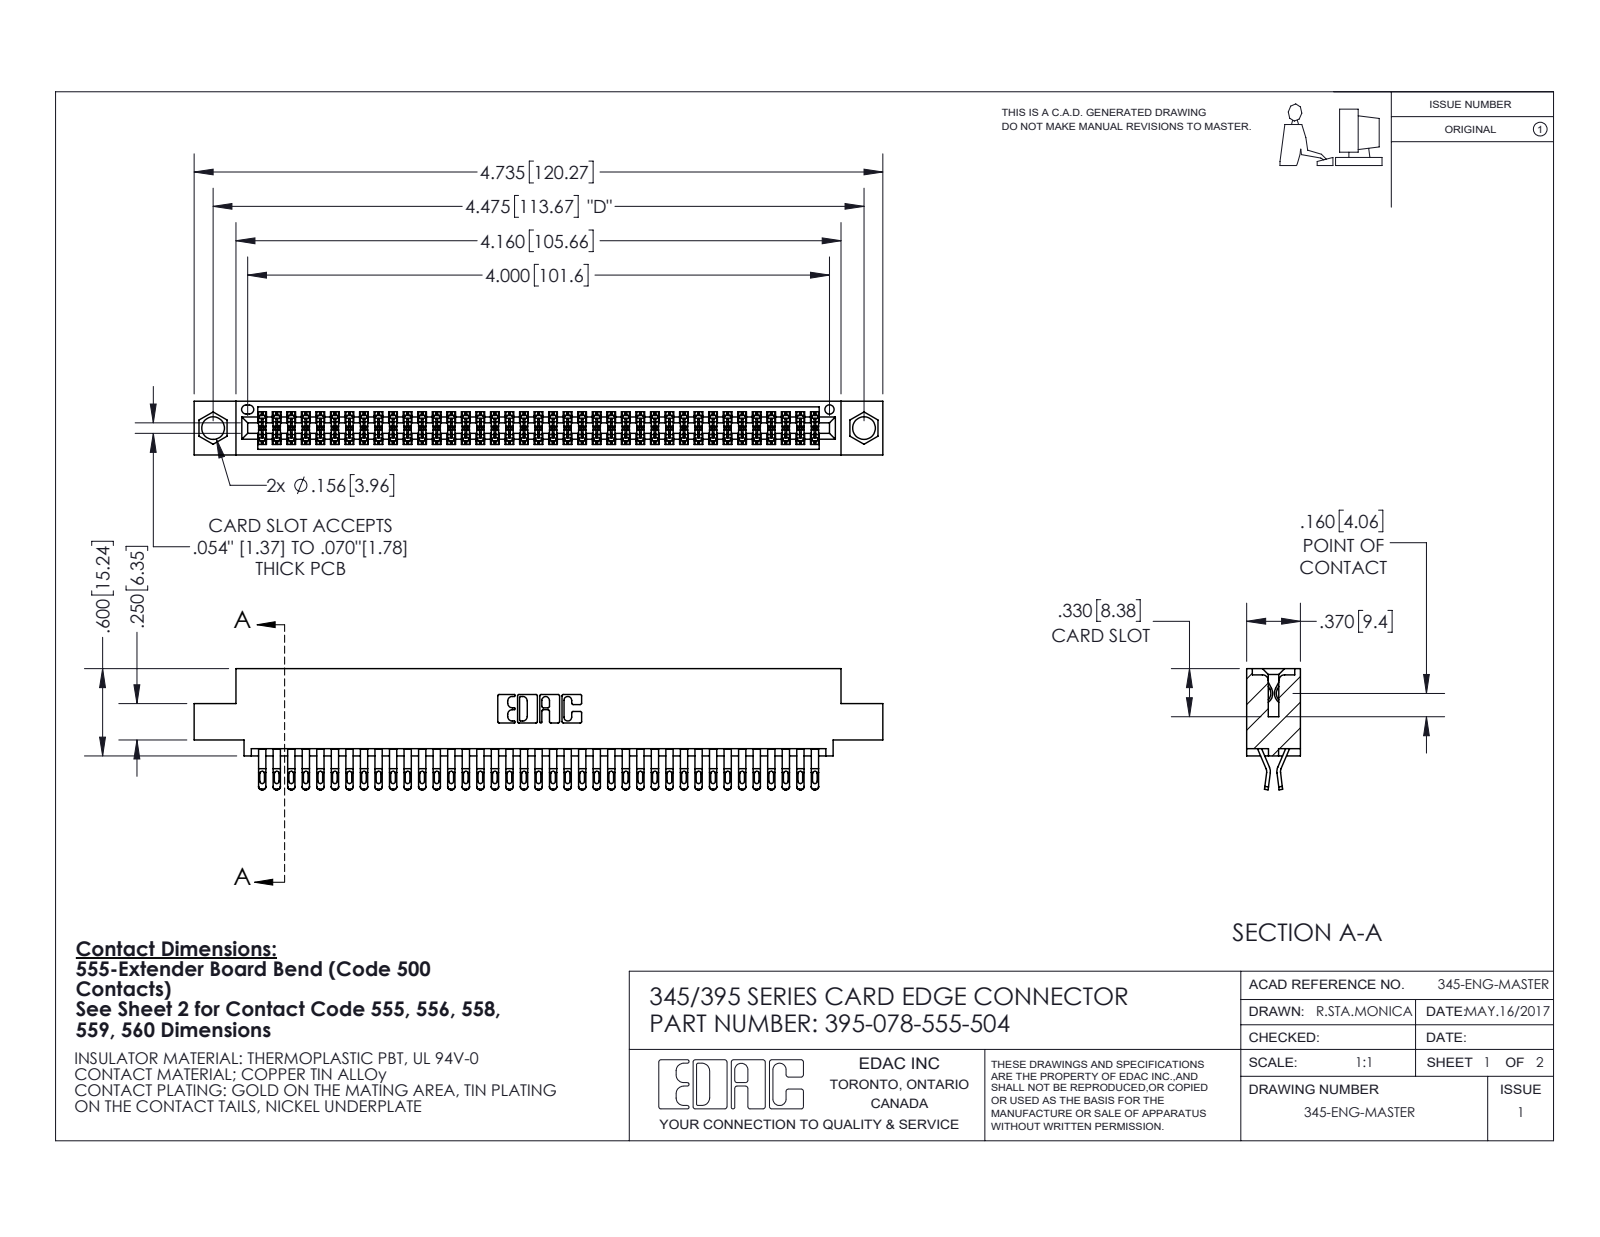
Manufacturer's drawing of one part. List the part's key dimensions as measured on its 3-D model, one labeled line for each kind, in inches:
Part name (STEP PRODUCT): 345-292-001_555 Tail; 345 Part_0.110 Offset - 0.156 Dia-TI; 395-078-555-504
STEP written by: SolidWorks 2020 (CONFIG_CONTROL_DESIGN)
Units: inches
Bodies: 79 solids, 4512 faces (2516 planar, 1996 cylindrical, 0 other)
Overall size (bounding box): 4.735 × 0.832 × 0.37
Volume: 0.714 in³ · Surface area: 27.86 in²
Round holes (diameter × count): ⌀0.156 ×2, ⌀0.064 ×1
Partial cylindrical surfaces — rounded edges, fillets, slot ends (radius × count): R0.016 ×195, R0.006 ×156, R0.02 ×156, R0.01 ×22, R0.007 ×6, R0.031 ×6, R0.026 ×3, R0.01 ×2
Main face-to-face distances: 0.298, 0.072, 0.025, 0.37, 0.2, 0.098, 0.272, 0.225, 0.175, 0.149
Hole centre spacings: 0.27, 4.239, 4.475
